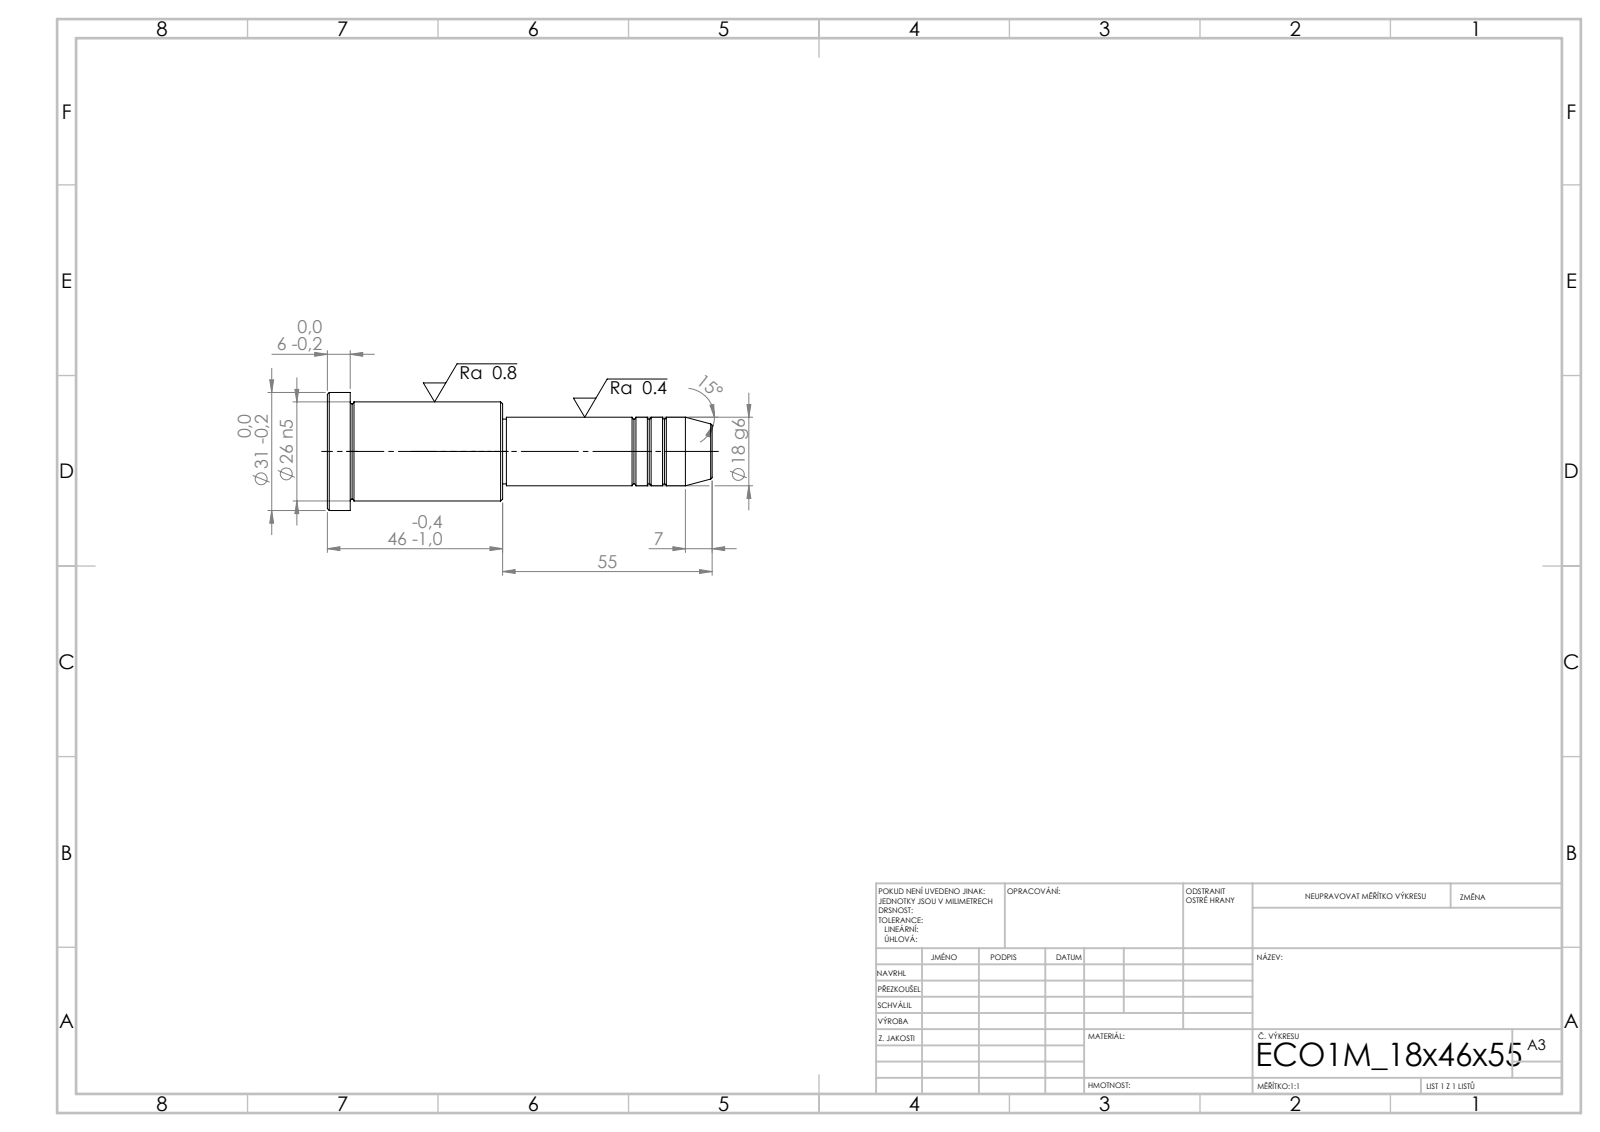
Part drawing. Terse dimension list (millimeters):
written by: SolidWorks 2019 (CONFIG_CONTROL_DESIGN)
unit: mm
bodies: 1 solid, 43 faces (5 planar, 14 cylindrical, 24 other)
size: 101 × 31 × 31
volume: 39 269 mm³; area: 8 472 mm²
bosses: 1× ⌀31, 1× ⌀26, 1× ⌀18, 1× ⌀17
face distances: 46, 40, 6, 55, 95, 101, 54, 1, 41, 47
